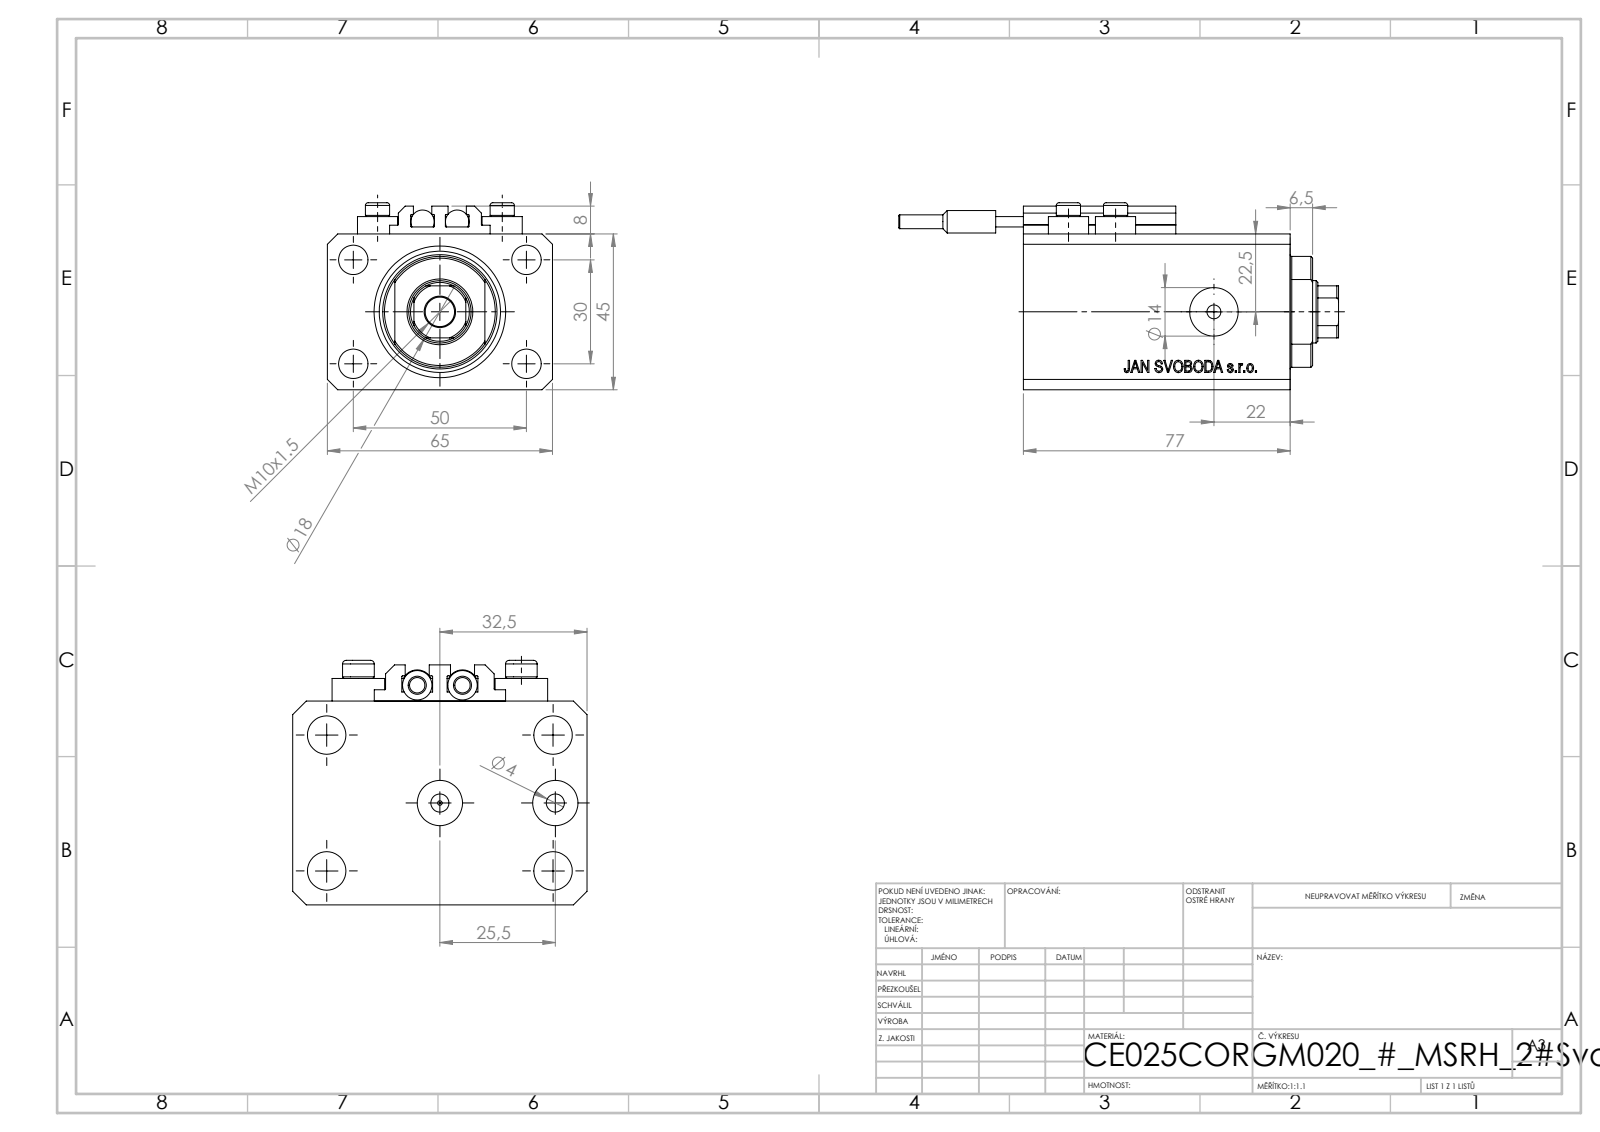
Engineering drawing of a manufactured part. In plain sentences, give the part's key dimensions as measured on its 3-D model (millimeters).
The part is named "SWITCH_V250CE; V250CE_VC_C; V250CE_C_VCP; ALLEN BOLT V250CE (+1 more)". Its 3-D file was written by "SolidWorks 2019 (CONFIG_CONTROL_DESIGN)". It is 10 solids with 1094 faces: 536 planar, 104 cylindrical and 454 other. Overall it measures 127 by 65 by 54 millimeters. Its volume is 215 074 cubic millimeters and its surface area 60 430 square millimeters. Round holes: 8 of diameter 4, 5 of diameter 8.5, 2 of diameter 10, 2 of diameter 14, 1 of diameter 1.25, 1 of diameter 18, 1 of diameter 25, 1 of diameter 38. Round bosses or shafts: 4 of diameter 11.6, 4 of diameter 7, 2 of diameter 6.8, 2 of diameter 6.5, 2 of diameter 4. Partial cylindrical surfaces (rounded edges, fillets, slot ends): 10 of radius 0.2, 1 of radius 8.5, 1 of radius 16. The main face-to-face distances are 45, 65, 14, 77, 63, 3, 47, 6.9, 56.1, 70.1. The hole center spacings are 29.15, 13.6, 15.01, 30, 36, 38.48, 50, 52.68.
